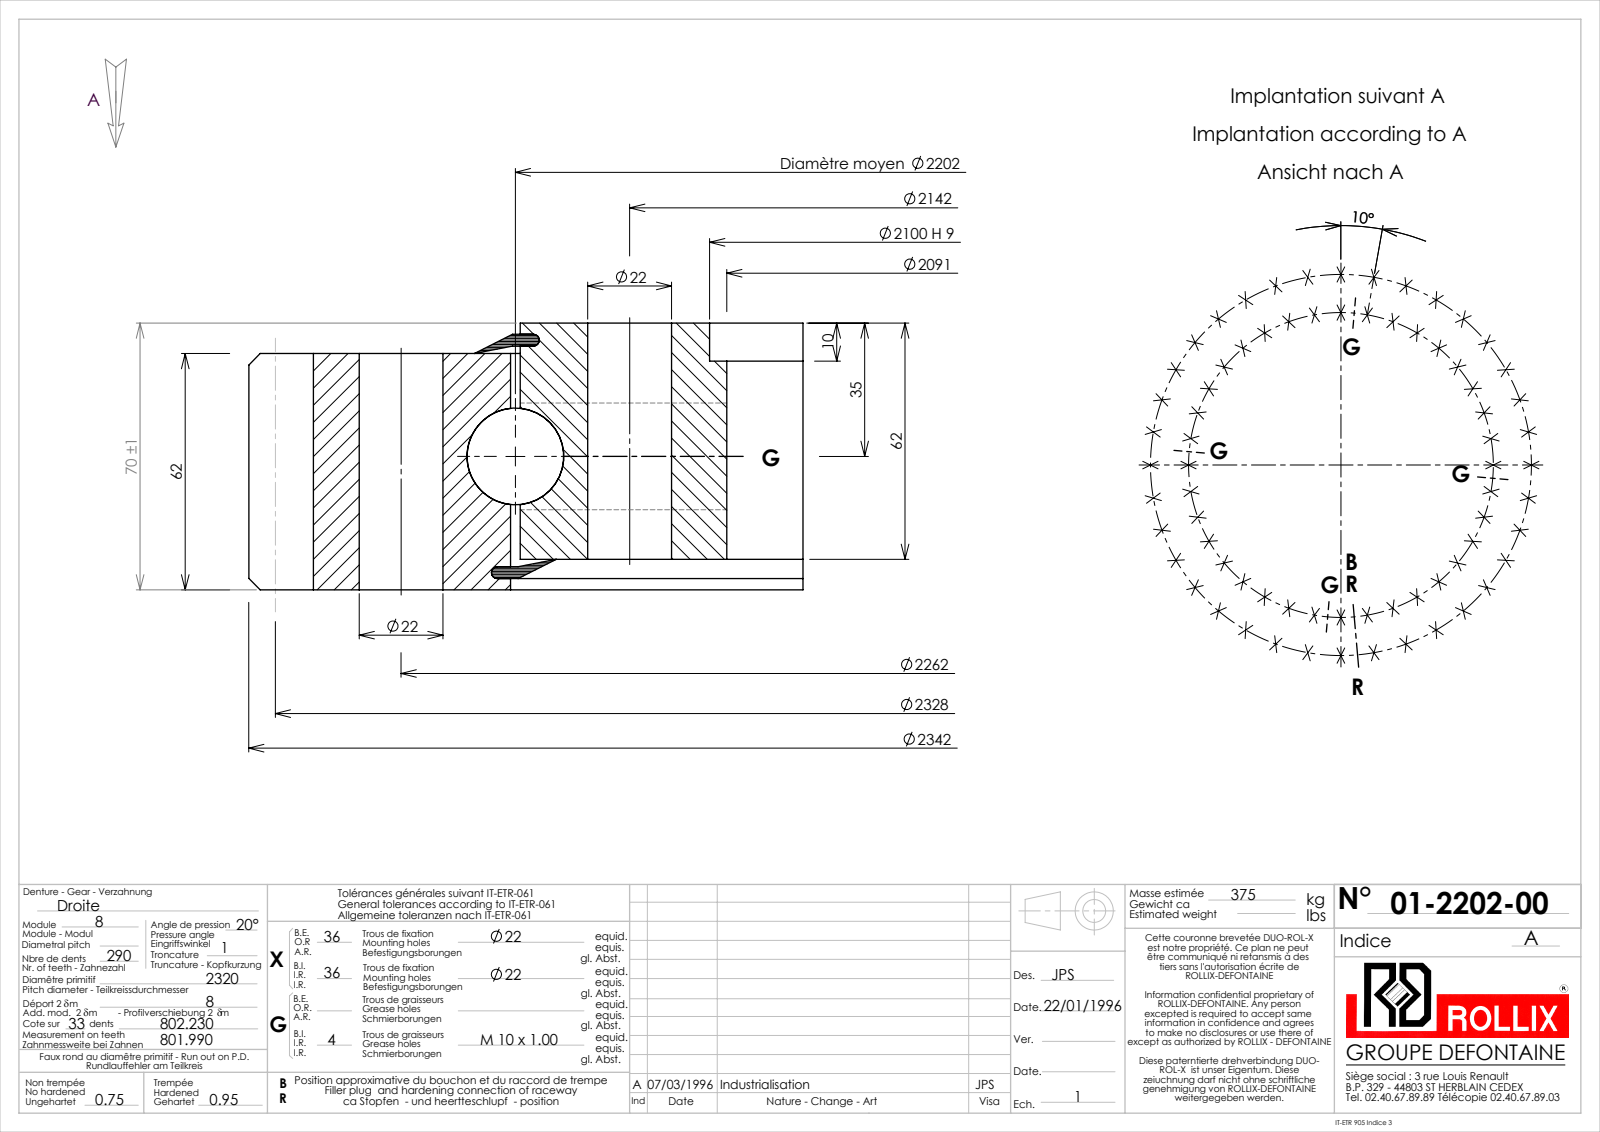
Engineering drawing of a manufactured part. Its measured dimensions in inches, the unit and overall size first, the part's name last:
Units: inches
Overall size (bounding box): 92.205 × 92.202 × 2.756
Round holes (diameter × count): ⌀0.866 ×72, ⌀0.354 ×4, ⌀82.323 ×1, ⌀82.677 ×1, ⌀86.793 ×1
Round bosses / shafts (diameter × count): ⌀86.593 ×1
Partial cylindrical surfaces — rounded edges, fillets, slot ends (radius × count): R45.433 ×1, R46.102 ×1
Main face-to-face distances: 2.441, 0.315, 2.126, 2.756, 0.238, 2.518, 0.077, 2.203, 0.116, 2.64
Hole centre spacings: 15.464, 51.08, 30.459, 72.95, 87.702, 77.124, 86.02, 37.636
Volume: 2 733 in³ · Surface area: 7 435 in²
Bodies: 5 solids, 1950 faces (593 planar, 749 cylindrical, 608 other)
Part name (STEP PRODUCT): 01-2202-00
STEP written by: SolidWorks 2016 (CONFIG_CONTROL_DESIGN)
